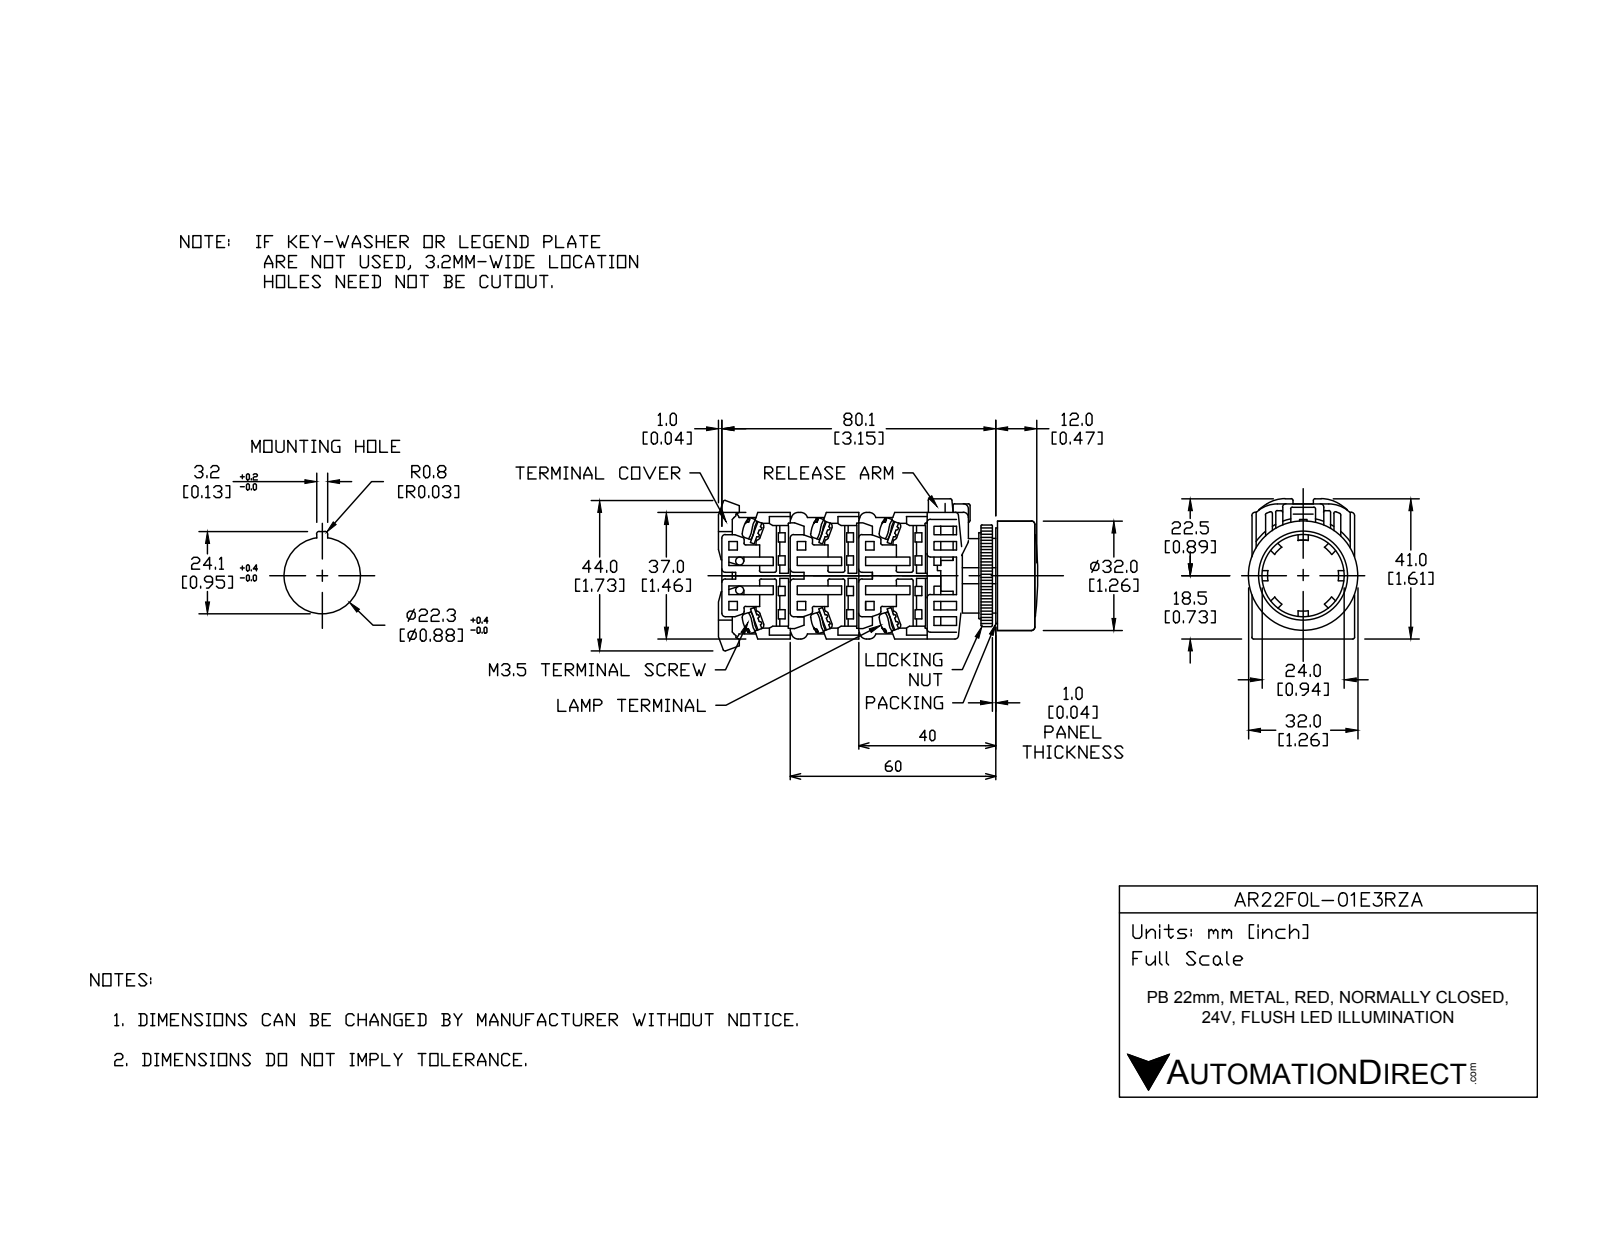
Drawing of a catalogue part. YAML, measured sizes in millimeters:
part_name: "AR22F0L-01E3RZA"
step_written_by: "SolidWorks 2017 (AUTOMOTIVE_DESIGN)"
units: millimeters
bodies: {solids: 18, faces: 475, planar: 329, cylindrical: 111, other: 35}
overall_size: [52.75, 43.81, 32]
volume: 36367
surface_area: 24064
round_holes:
  - {diameter: 21.8, count: 1}
  - {diameter: 22, count: 1}
  - {diameter: 25, count: 1}
  - {diameter: 31, count: 1}
round_bosses_or_shafts:
  - {diameter: 5, count: 4}
  - {diameter: 32, count: 1}
  - {diameter: 30.5, count: 1}
  - {diameter: 29.8, count: 1}
  - {diameter: 24, count: 1}
  - {diameter: 23.8, count: 1}
  - {diameter: 21.75, count: 1}
  - {diameter: 17, count: 1}
partial_cylinders:
  - {radius: 0.5, count: 39}
  - {radius: 1.75, count: 8}
  - {radius: 5, count: 4}
  - {radius: 4, count: 2}
  - {radius: 16.59, count: 1}
  - {radius: 17.59, count: 1}
face_to_face_distances: [1, 18, 28.5, 48.5, 20, 29, 3, 2, 21, 0.5]
